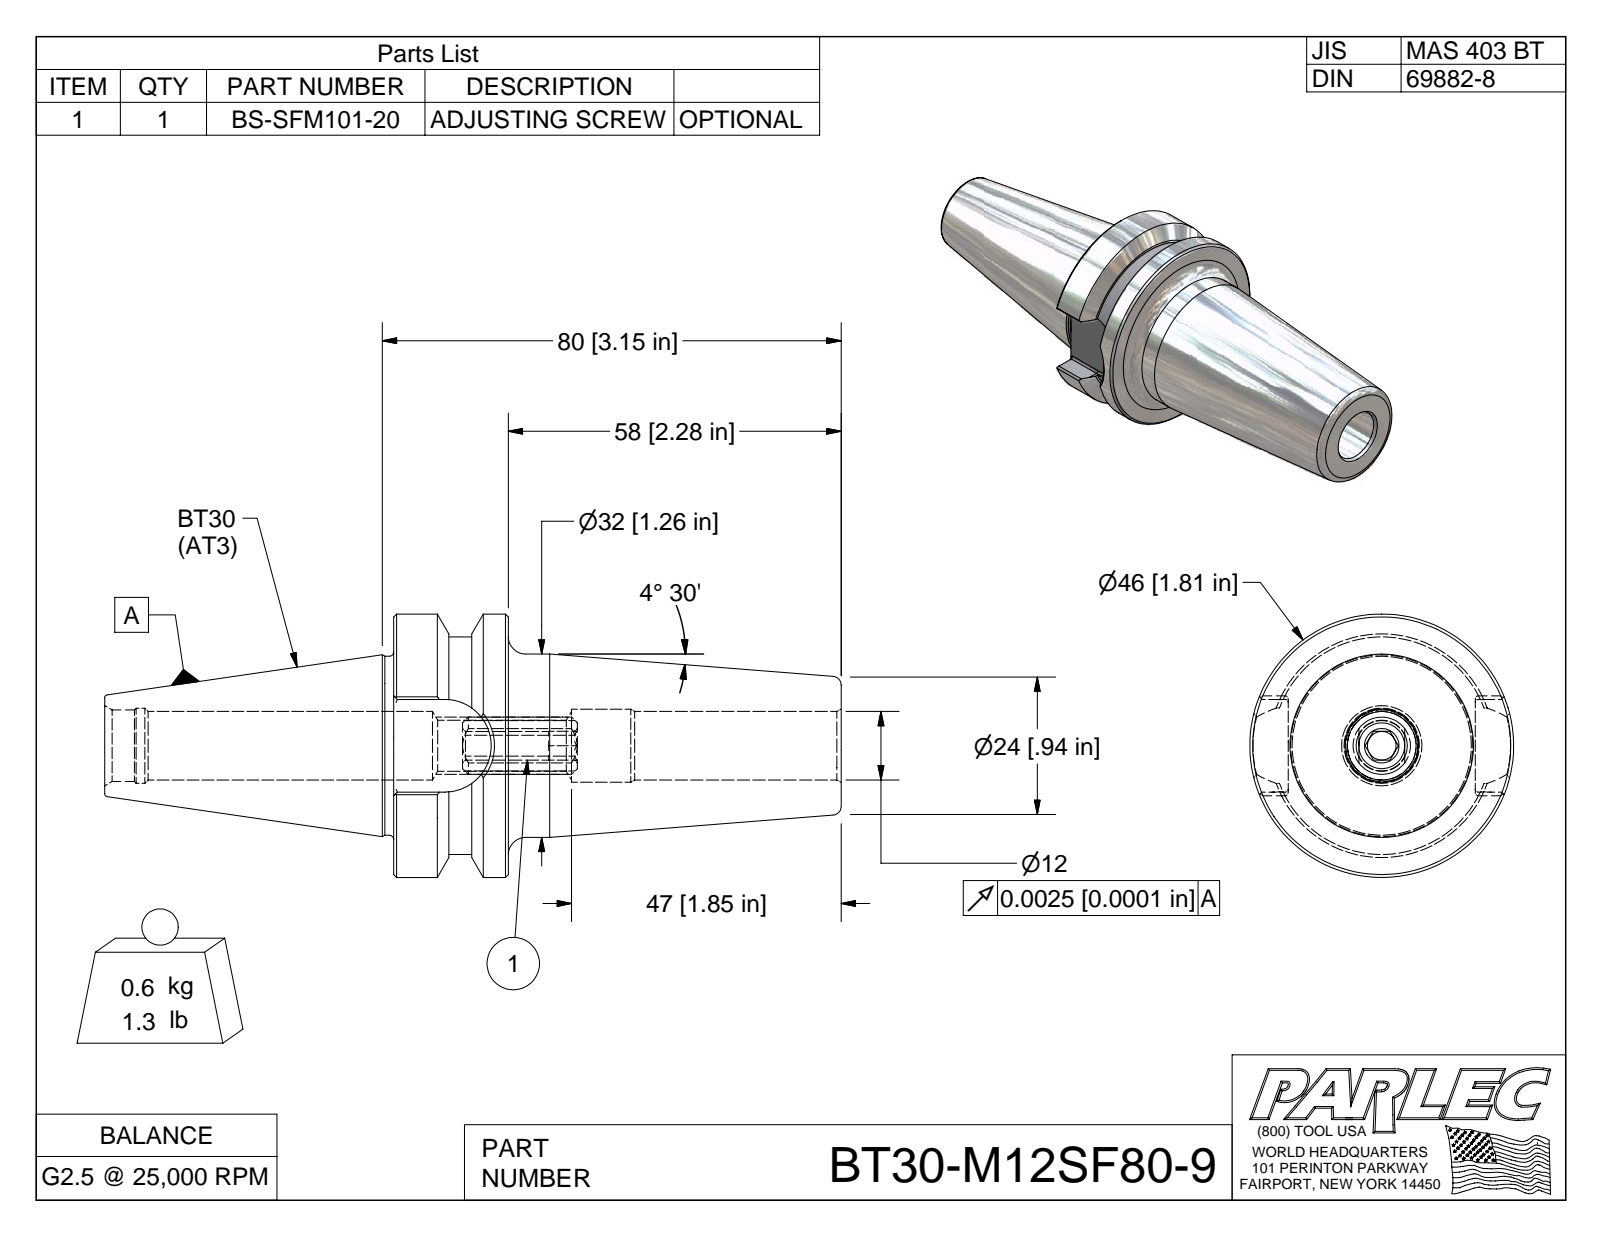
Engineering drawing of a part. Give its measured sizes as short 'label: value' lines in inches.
name: BT30-M12SF80-9; BT30-M12SF80-9-1; BS-SFM101-20
written by: Autodesk Inventor 2009 (AUTOMOTIVE_DESIGN)
unit: in
bodies: 2 solids, 92 faces (35 planar, 22 cylindrical, 35 other)
size: 5.056 × 1.811 × 1.811
volume: 4.756 in³; area: 31.35 in²
holes: 1× ⌀0.471, 1× ⌀0.501, 1× ⌀0.517
bosses: 1× ⌀1.811, 1× ⌀1.26, 1× ⌀1.23
rounds: 8× R0.02, 1× R0.197, 1× R0.319, 1× R0.748
face distances: 0.787, 0.484, 0.799, 1.283, 3.072, 2.285, 0.315, 1.984, 2.771, 5.056
